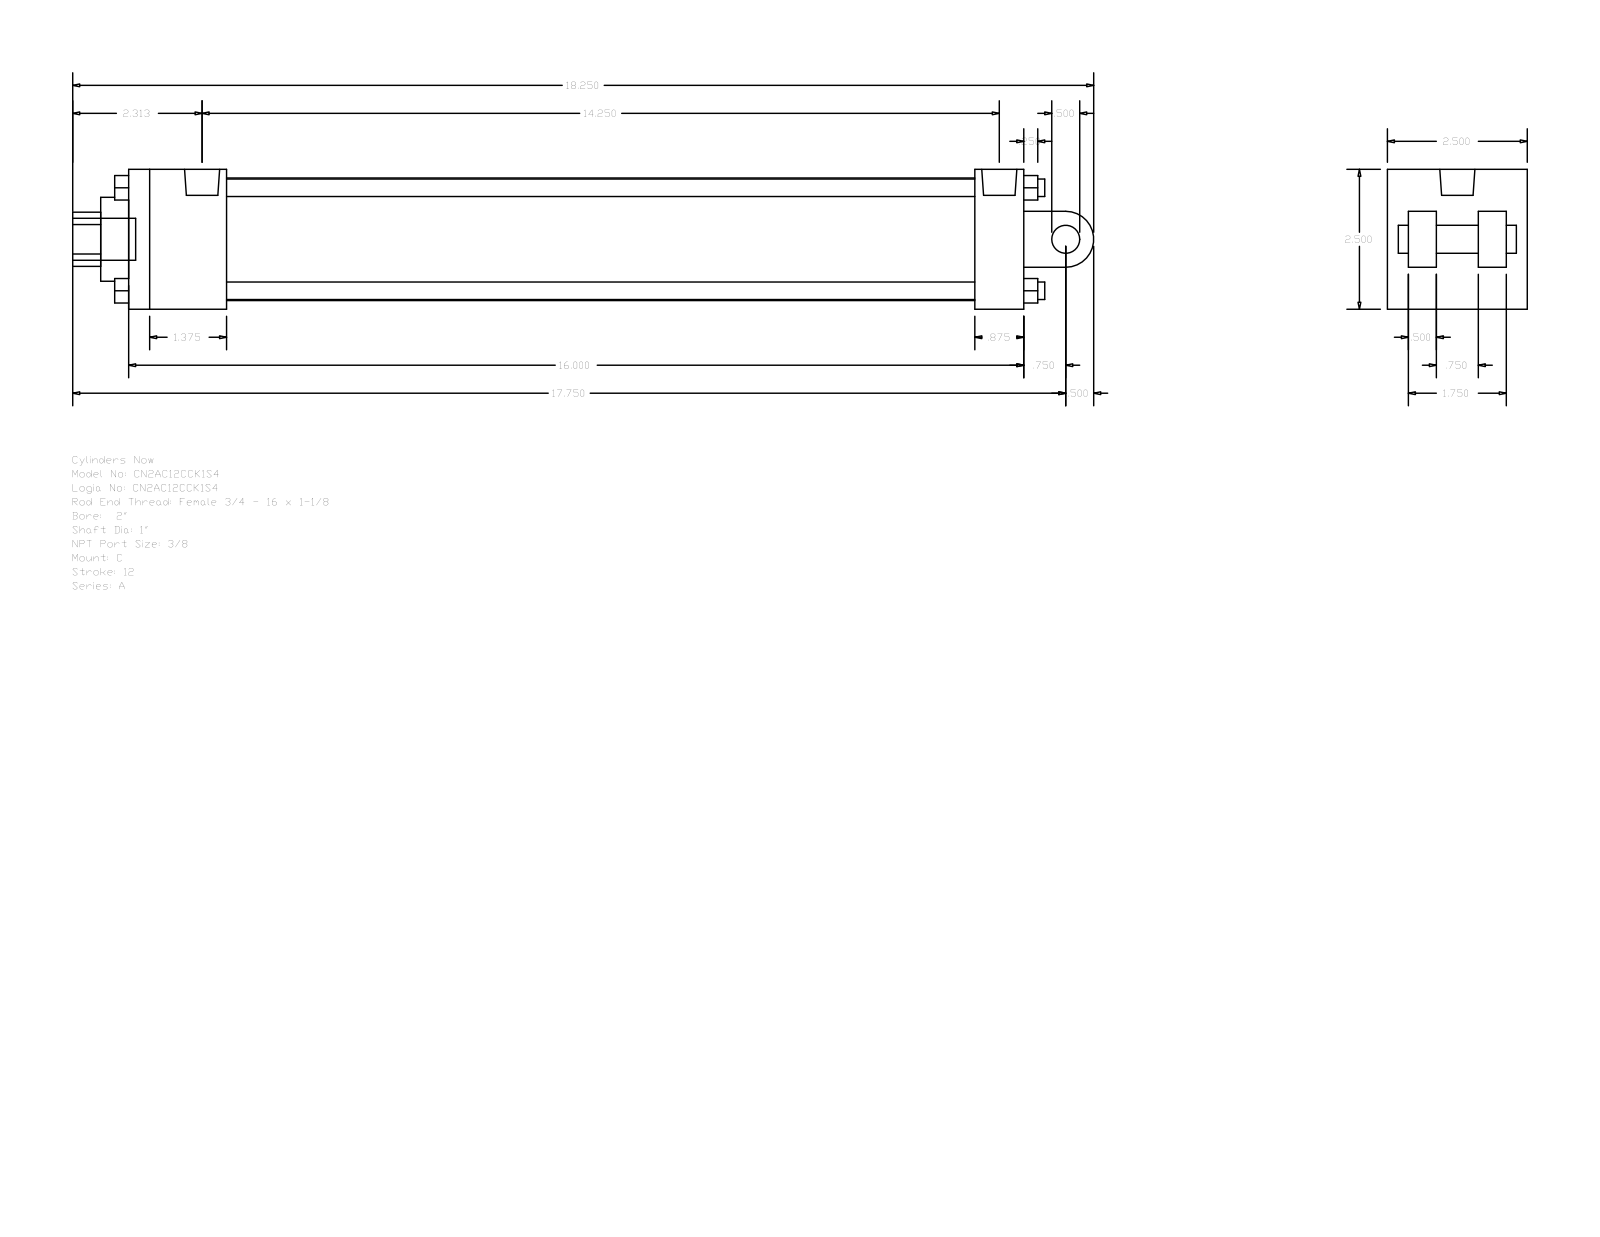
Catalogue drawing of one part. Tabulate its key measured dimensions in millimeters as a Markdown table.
| quantity | value |
| --- | --- |
| part name | A_C__0200_1 |
| STEP written by | GSSL Pune (CONFIG_CONTROL_DESIGN) |
| units | millimeters |
| bodies | 0 solids, 135 faces (102 planar, 33 cylindrical, 0 other) |
| overall size | 463.55 × 63.5 × 63.5 |
| round holes (diameter × count) | 5.56 × 2, 15.93 × 1, 25.4 × 1, 38.1 × 1, 55.63 × 1 |
| round bosses / shafts (diameter × count) | 7.94 × 4, 5.56 × 2, 19.05 × 1, 15.93 × 1, 12.7 × 1 |
| partial cylindrical surfaces (radius × count) | 12.29 × 1, 12.7 × 1 |
| main face-to-face distances | 63.5, 406.4, 44.45, 12.7, 9.52, 41.28, 361.95, 384.17, 339.72, 22.23 |
| hole center spacings | 3.98 |
